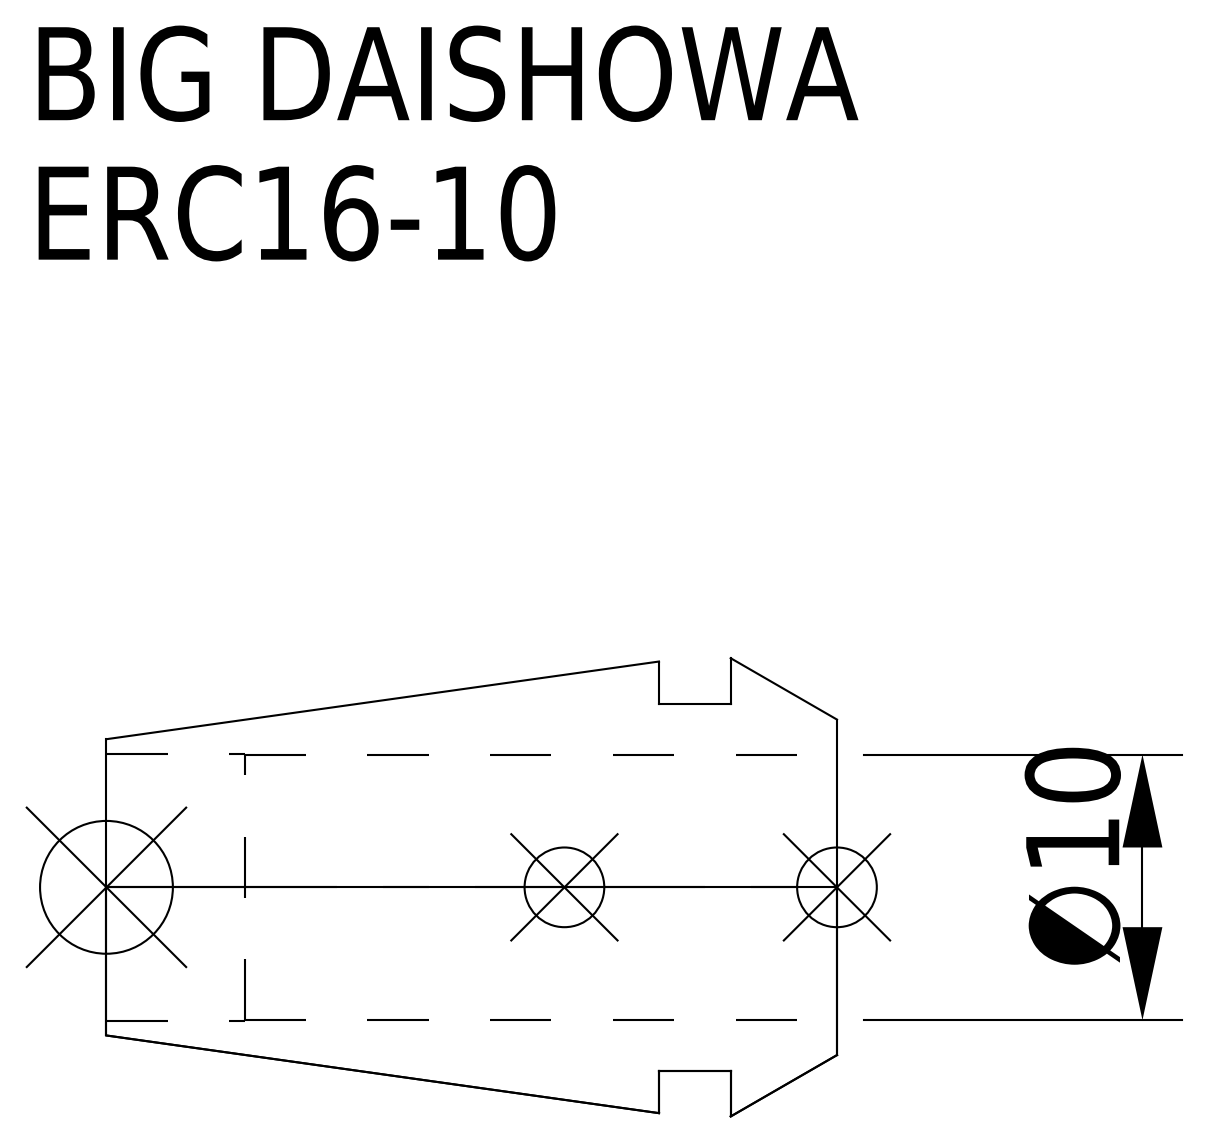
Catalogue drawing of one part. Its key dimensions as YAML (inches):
part_name: "ERC16-10"
step_written_by: "CREO PARAMETRIC BY PTC INC, 2016380 (AUTOMOTIVE_DESIGN)"
units: inches
bodies: {solids: 1, faces: 15, planar: 5, cylindrical: 6, other: 4}
overall_size: [1.083, 0.679, 0.679]
volume: 0.136
surface_area: 3.65
round_holes:
  - {diameter: 0.394, count: 1}
  - {diameter: 0.396, count: 1}
round_bosses_or_shafts:
  - {diameter: 0.543, count: 1}
face_to_face_distances: [0.106, 0.157, 0.264, 1.083, 0.925, 0.819, 0.878, 0.72, 0.614, 0.205]
